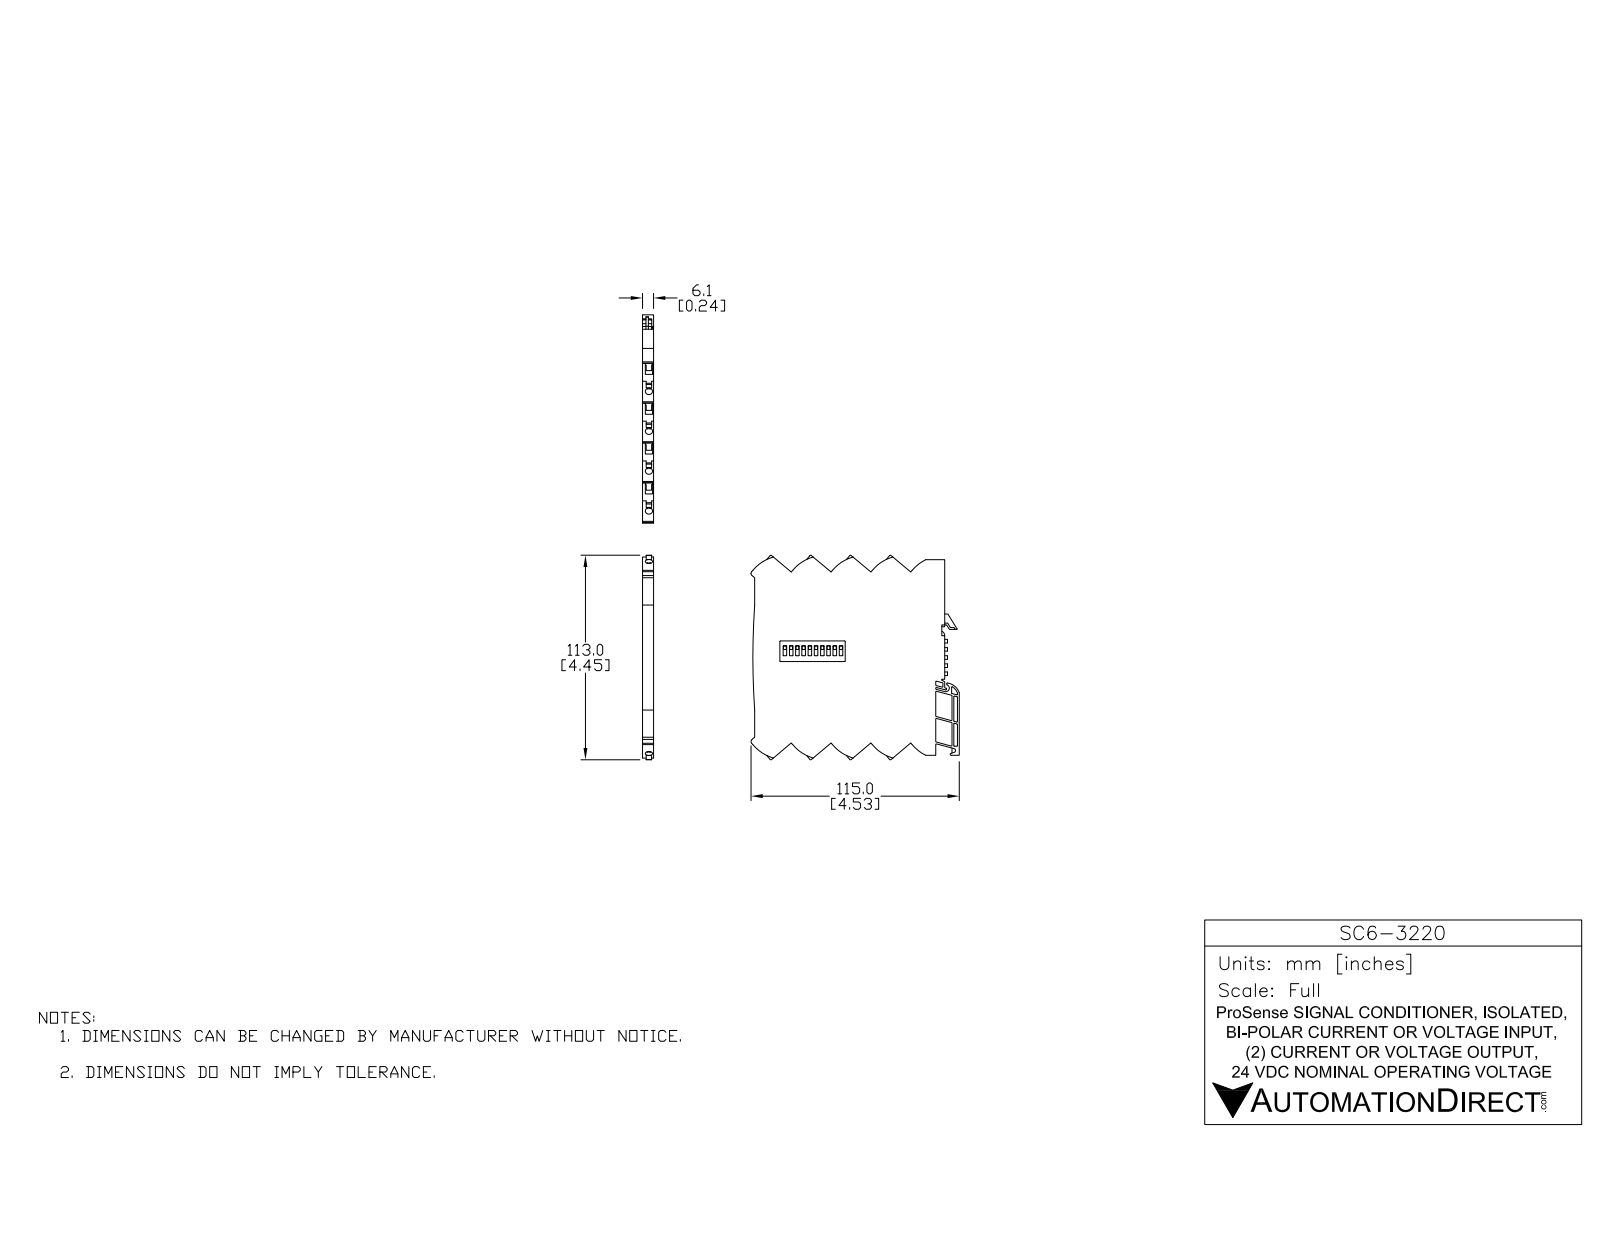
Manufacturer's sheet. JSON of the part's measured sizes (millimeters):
{"part_name": "SC6-3220", "step_written_by": "SolidWorks 2017 (AUTOMOTIVE_DESIGN)", "units": "millimeters", "bodies": {"solids": 1, "faces": 644, "planar": 443, "cylindrical": 117, "other": 84}, "overall_size": [115, 112.99, 6.1], "volume_mm3": 64771, "surface_area_mm2": 28345, "round_holes": [[4, 8]], "partial_cylinders_radius": [[0.3, 33], [0.5, 10], [1.5, 10], [23.31, 10], [0.2, 2], [0.57, 1], [1.08, 1], [1.47, 1]], "face_to_face_distances": [6.1, 1, 3, 4, 2.05, 3.05, 5.1, 14.14, 1.05, 4.05], "hole_center_spacings": [14.14, 28.28, 14.15, 42.42]}
